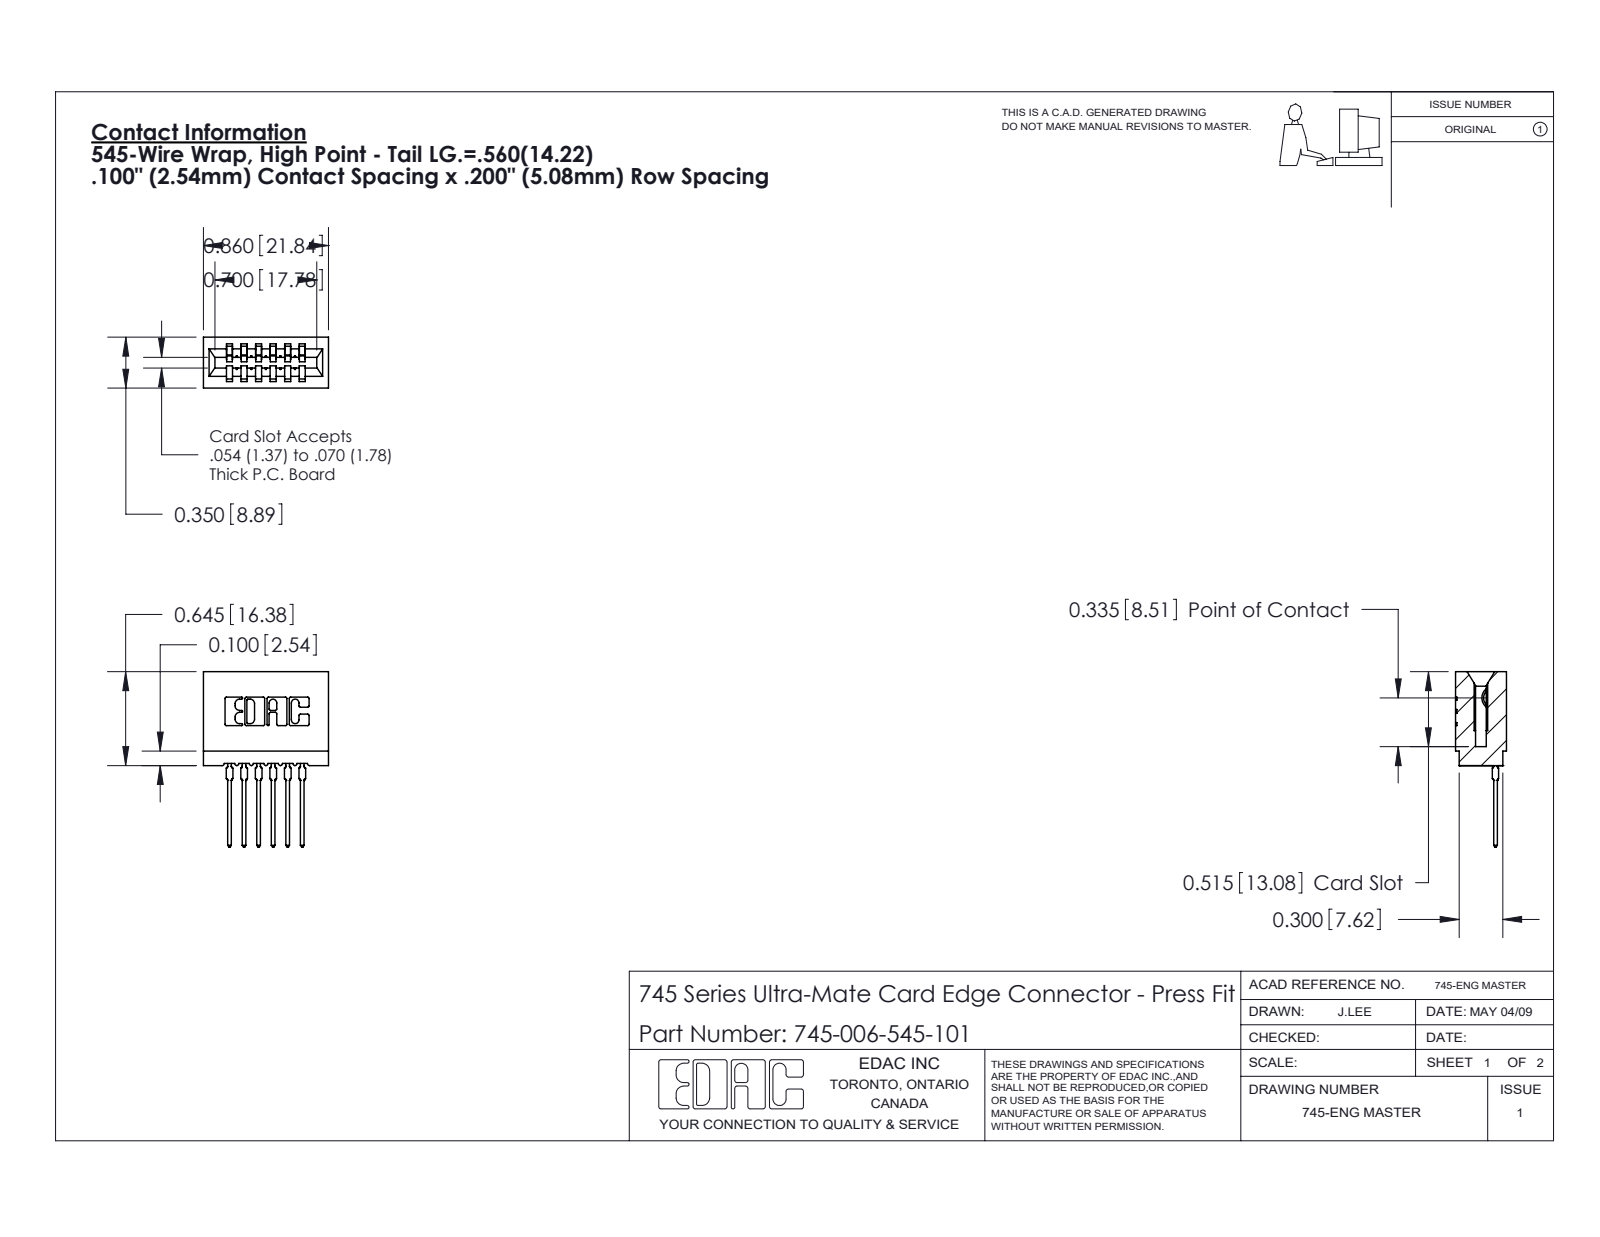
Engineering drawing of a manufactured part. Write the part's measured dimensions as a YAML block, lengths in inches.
part_name: "745-006-545-101; 745-292-001_545; 745 Part_Insulator Option - 01"
step_written_by: "SolidWorks 2020 (CONFIG_CONTROL_DESIGN)"
units: inches
bodies: {solids: 7, faces: 767, planar: 457, cylindrical: 154, other: 156}
overall_size: [1.206, 0.86, 0.35]
volume: 0.131
surface_area: 5.238
partial_cylinders:
  - {radius: 0.01, count: 22}
  - {radius: 0.015, count: 12}
  - {radius: 0.021, count: 12}
  - {radius: 0.007, count: 6}
  - {radius: 0.031, count: 6}
  - {radius: 0.005, count: 4}
  - {radius: 0.011, count: 4}
  - {radius: 0.026, count: 3}
face_to_face_distances: [0.1, 0.2, 0.3, 0.042, 0.142, 0.058, 0.242, 0.4, 0.158, 0.35]
